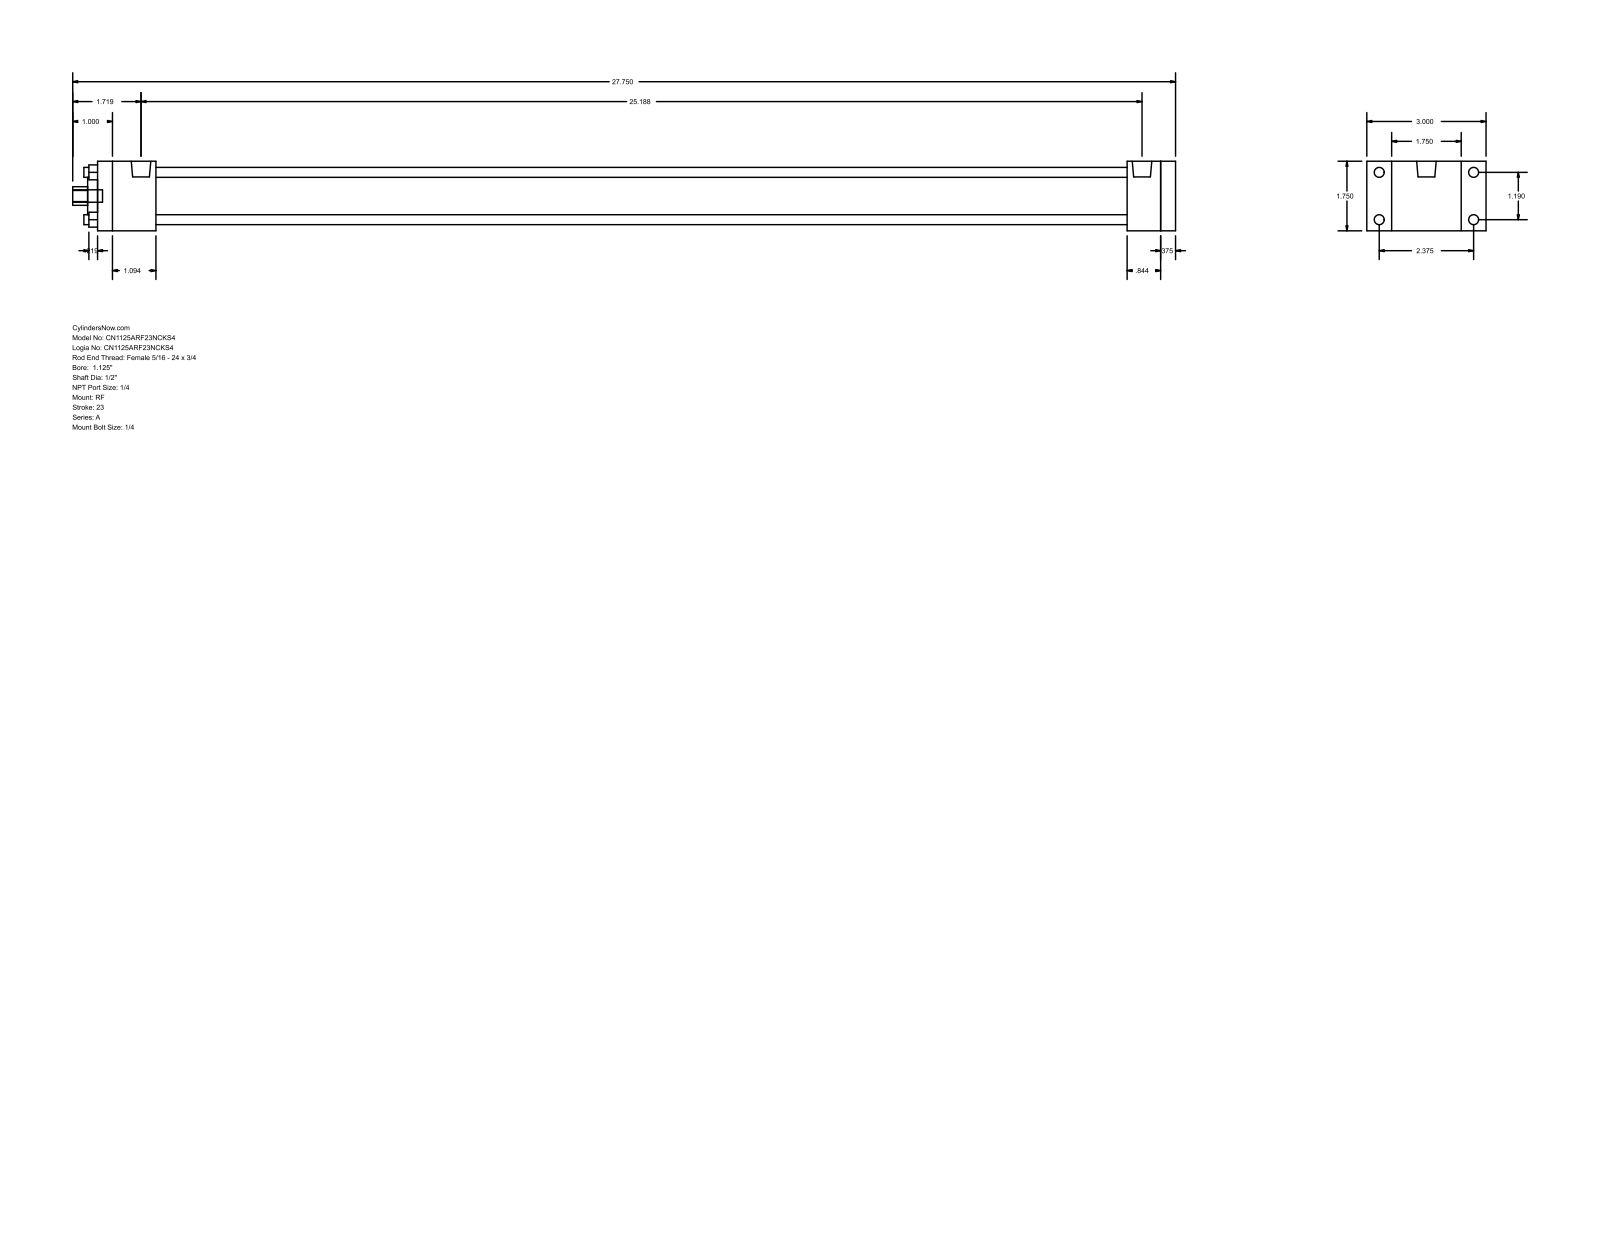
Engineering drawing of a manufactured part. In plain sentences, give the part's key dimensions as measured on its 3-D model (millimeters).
The part is named "A_RF__0112_0.5". Its 3-D file was written by "GSSL Pune (CONFIG_CONTROL_DESIGN)". It is 0 solids with 92 faces: 64 planar, 28 cylindrical and 0 other. Overall it measures 704.85 by 76.2 by 44.45 millimeters. Round holes: 4 of diameter 6.35, 1 of diameter 12.7, 1 of diameter 23.81, 1 of diameter 31.88. Round bosses or shafts: 4 of diameter 6.35, 4 of diameter 5.56, 2 of diameter 12.49, 1 of diameter 7.94. Partial cylindrical surfaces (rounded edges, fillets, slot ends): 1 of radius 5.94. The main face-to-face distances are 44.46, 9.52, 679.45, 688.97, 37.3, 658.01, 620.71, 642.15, 651.67, 21.44. The hole center spacings are 21.37, 30.22, 42.74.
